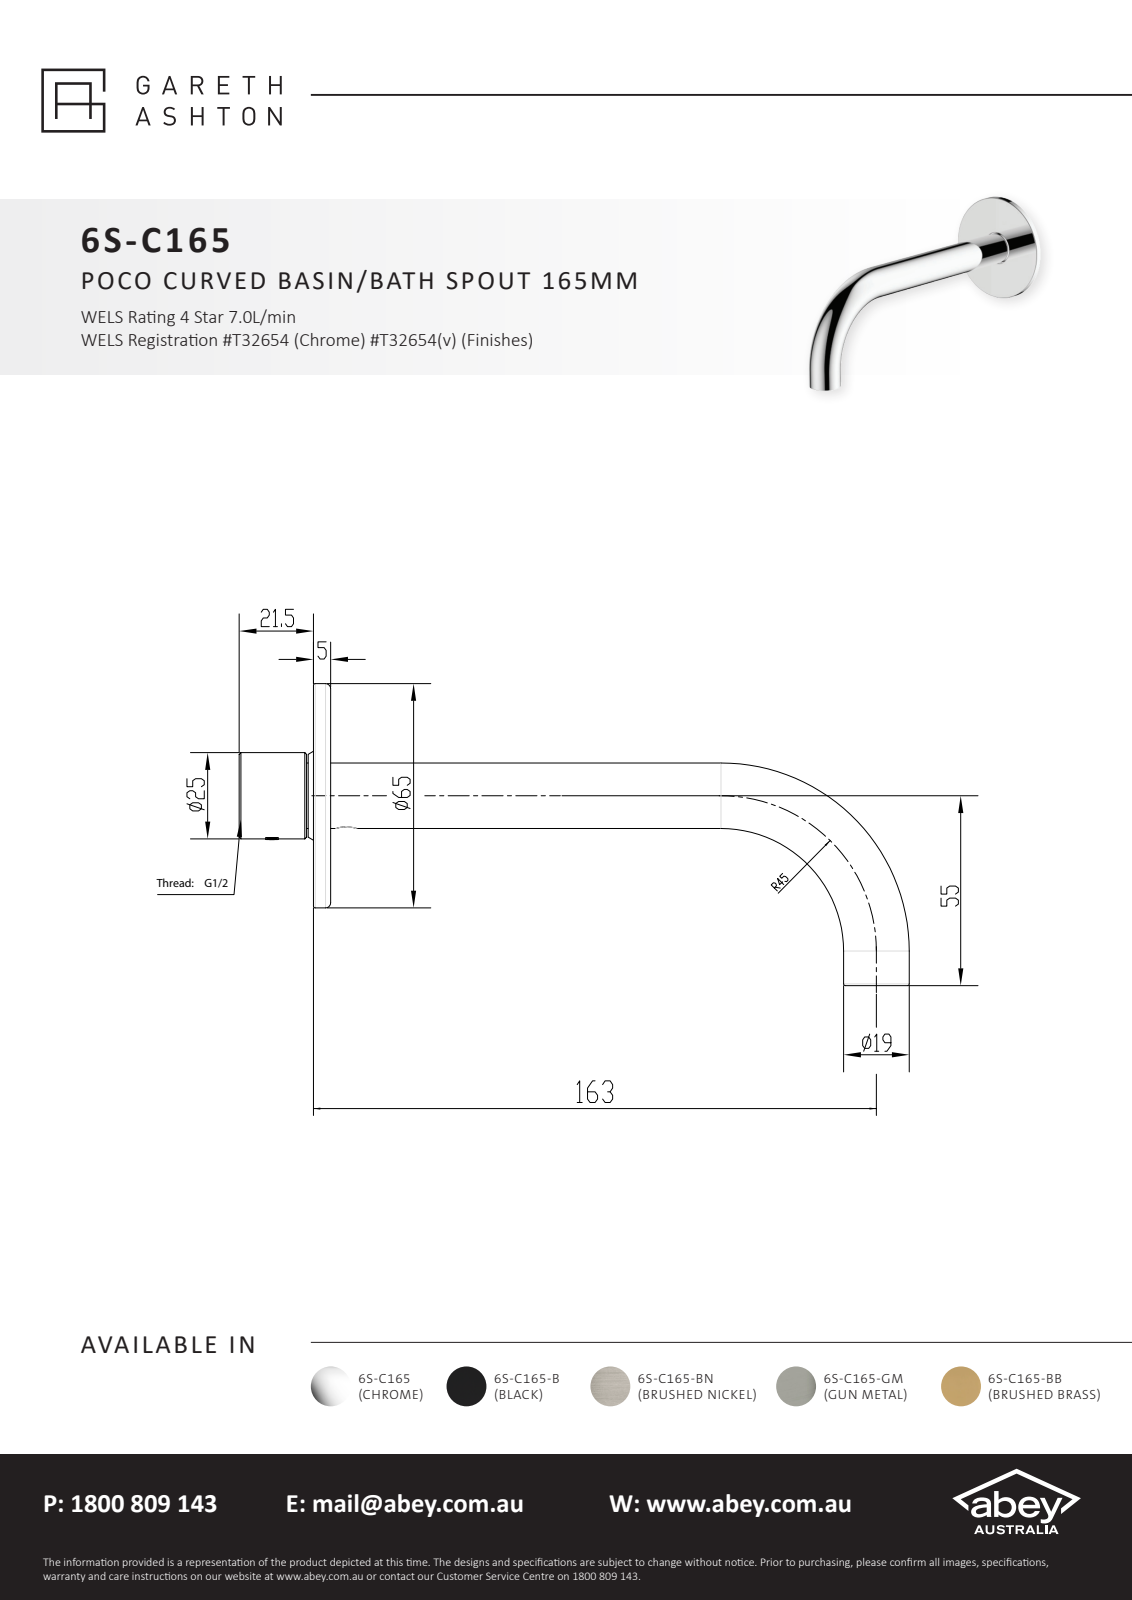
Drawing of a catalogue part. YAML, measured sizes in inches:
part_name: "63043-04-00; 63043-01-01; 63043-01-02; 63043-01-00_ASM (+8 more)"
step_written_by: "CREO PARAMETRIC BY PTC INC, 2018420 (CONFIG_CONTROL_DESIGN)"
units: inches
bodies: {solids: 11, faces: 4693, planar: 4070, cylindrical: 339, other: 284}
overall_size: [10.098, 5.083, 2.559]
volume: 2.62
surface_area: 131.4
round_holes:
  - {diameter: 0.217, count: 2}
  - {diameter: 0.157, count: 1}
  - {diameter: 0.163, count: 1}
  - {diameter: 0.425, count: 1}
  - {diameter: 0.453, count: 1}
  - {diameter: 0.476, count: 1}
  - {diameter: 0.484, count: 1}
  - {diameter: 0.512, count: 1}
  - {diameter: 0.52, count: 1}
  - {diameter: 0.528, count: 1}
  - {diameter: 0.571, count: 1}
  - {diameter: 0.591, count: 1}
round_bosses_or_shafts:
  - {diameter: 0.748, count: 2}
  - {diameter: 2.559, count: 1}
  - {diameter: 1.063, count: 1}
  - {diameter: 0.825, count: 1}
  - {diameter: 0.685, count: 1}
  - {diameter: 0.65, count: 1}
  - {diameter: 0.63, count: 1}
  - {diameter: 0.591, count: 1}
partial_cylinders:
  - {radius: 0.01, count: 4}
  - {radius: 0.209, count: 2}
  - {radius: 1.334, count: 2}
  - {radius: 0.079, count: 1}
  - {radius: 0.293, count: 1}
face_to_face_distances: [0.039, 0.157, 0.098, 0.276, 0.236, 0.02, 1.004, 0.079, 0.217, 0.787]
hole_center_spacings: [6.043]
